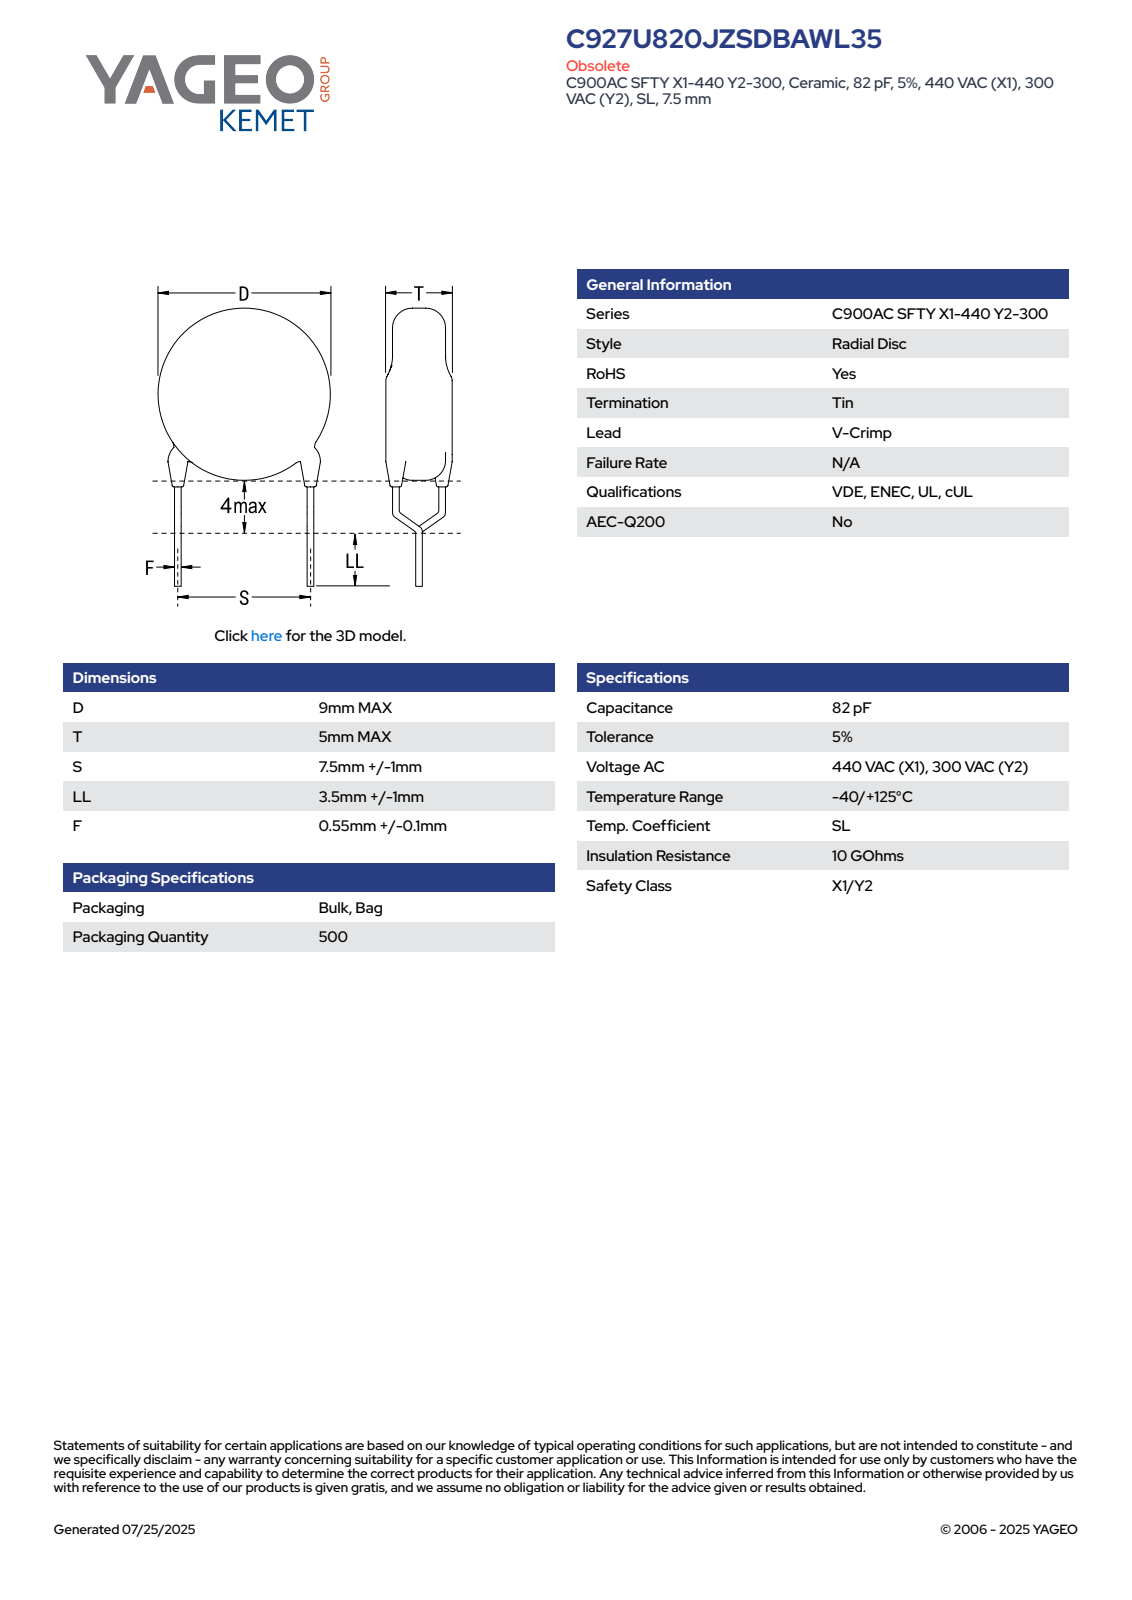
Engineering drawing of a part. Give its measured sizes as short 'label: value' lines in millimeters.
name: CCD_VCC900_D9T5S7.5LL4.5F0.65
written by: SolidWorks 2014 (AUTOMOTIVE_DESIGN)
unit: mm
bodies: 5 solids, 93 faces (65 planar, 16 cylindrical, 12 other)
size: 17.3 × 9 × 5
volume: 315 mm³; area: 296 mm²
bosses: 6× ⌀0.65, 1× ⌀9
face distances: 5, 7.4, 1.17, 13.38, 5.98, 12.21, 4.81, 0.32, 4.77, 3.47
